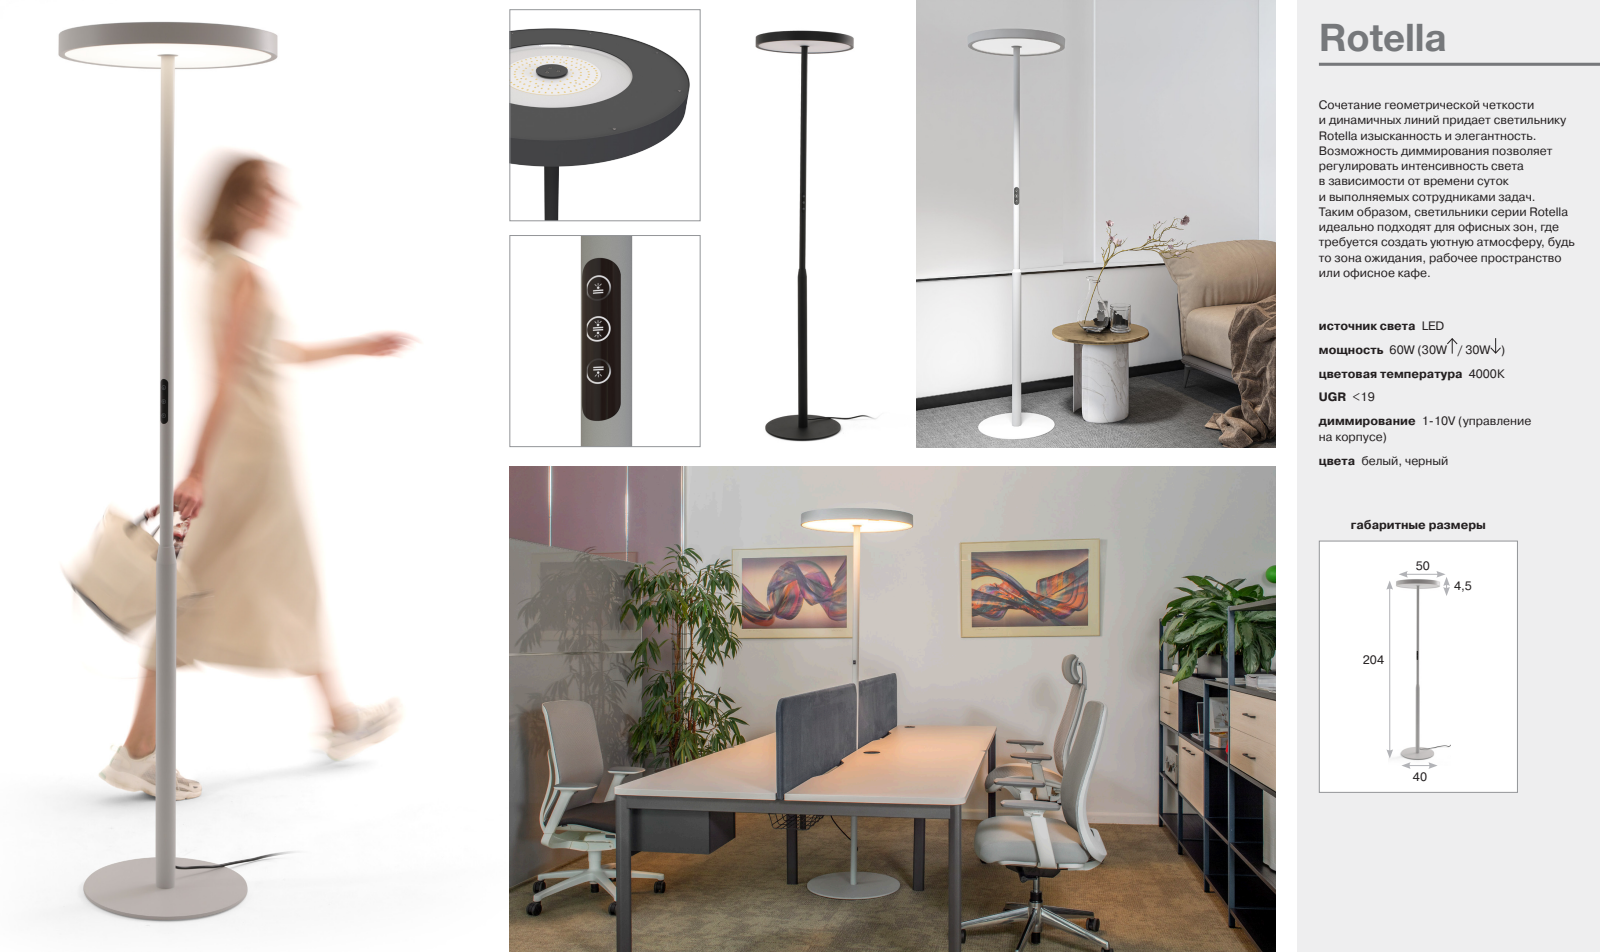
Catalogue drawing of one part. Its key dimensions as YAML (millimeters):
part_name: "DENGKUANG_133; LENGJINGBAN_125; KUOSANBAN_126; DUXINBAN_139 (+8 more)"
step_written_by: "PRO/ENGINEER BY PARAMETRIC TECHNOLOGY CORPORATION, 2013040 (CONFIG_CONTROL_DESIGN)"
units: millimeters
bodies: {solids: 38, faces: 3380, planar: 1214, cylindrical: 1344, other: 822}
overall_size: [2037.3, 921.65, 500]
volume: 2532000
surface_area: 2905000
round_holes:
  - {diameter: 4, count: 14}
  - {diameter: 3.5, count: 10}
  - {diameter: 5, count: 8}
  - {diameter: 5.5, count: 6}
  - {diameter: 8.5, count: 5}
  - {diameter: 4.5, count: 2}
  - {diameter: 5.2, count: 1}
  - {diameter: 29.96, count: 1}
  - {diameter: 33, count: 1}
  - {diameter: 33.5, count: 1}
  - {diameter: 35.08, count: 1}
  - {diameter: 36.2, count: 1}
round_bosses_or_shafts:
  - {diameter: 13.5, count: 192}
  - {diameter: 5, count: 10}
  - {diameter: 3, count: 9}
  - {diameter: 4, count: 8}
  - {diameter: 7, count: 4}
  - {diameter: 6.8, count: 4}
  - {diameter: 10.03, count: 3}
  - {diameter: 6.6, count: 2}
partial_cylinders:
  - {radius: 0.2, count: 130}
  - {radius: 0.3, count: 26}
  - {radius: 0.5, count: 22}
  - {radius: 0.1, count: 4}
  - {radius: 4, count: 4}
  - {radius: 0.15, count: 2}
  - {radius: 0.6, count: 2}
  - {radius: 0.62, count: 2}
face_to_face_distances: [31, 1.5, 38, 8, 2026.5, 1.2, 32.2, 7, 5.8, 39.5]
hole_center_spacings: [204.5, 151.56, 179.86, 235, 332.34, 379.88, 434.22, 61.5]
